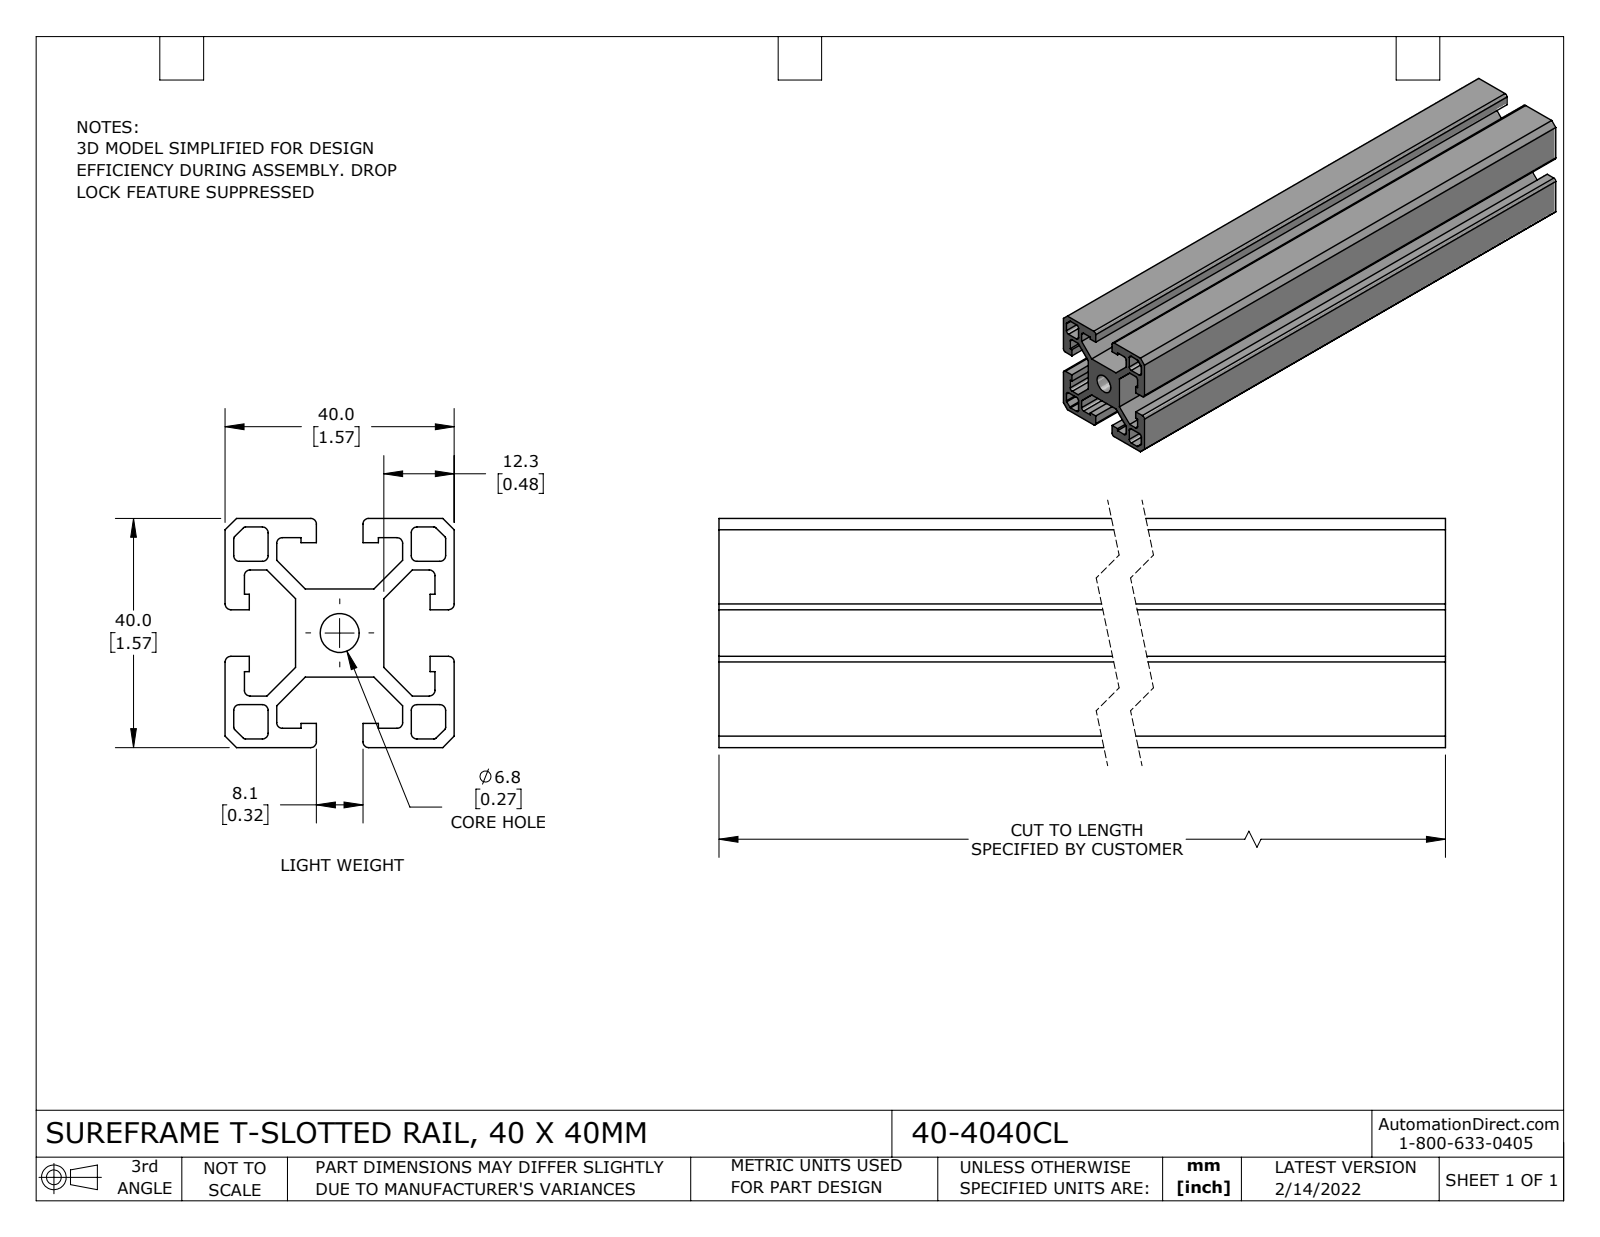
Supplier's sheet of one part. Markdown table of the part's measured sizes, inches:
| quantity | value |
| --- | --- |
| part name | 40-4040CL |
| STEP written by | SolidWorks 2021 (CONFIG_CONTROL_DESIGN) |
| units | inches |
| bodies | 1 solid, 124 faces (86 planar, 38 cylindrical, 0 other) |
| overall size | 8 × 1.575 × 1.575 |
| volume | 7.976 in³ |
| surface area | 145.6 in² |
| round holes (diameter × count) | 0.268 × 1 |
| partial cylindrical surfaces (radius × count) | 0.039 × 28, 0.02 × 8 |
| main face-to-face distances | 0.295, 1.575, 0.484, 1.091, 0.059, 1.22, 1.28, 0.189, 0.795, 0.094 |
